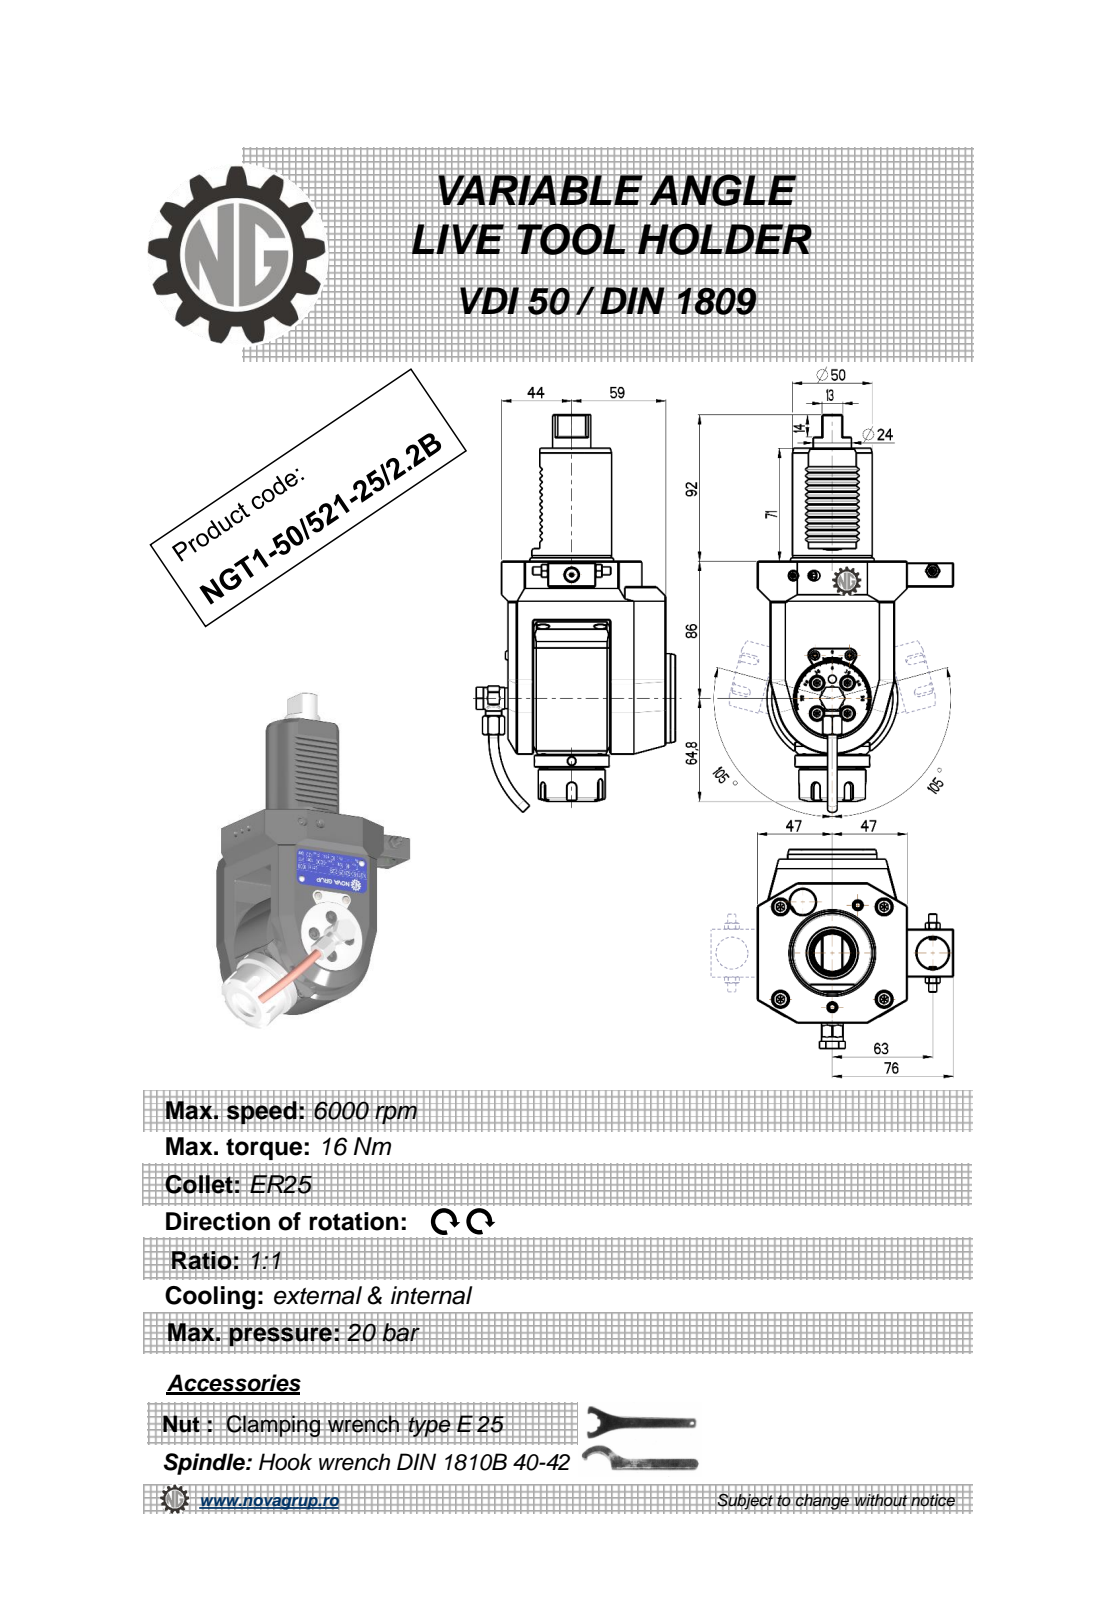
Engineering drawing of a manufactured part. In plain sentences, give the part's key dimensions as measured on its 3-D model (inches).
The part is named "NGT1_50_521_25_2_2B". Its 3-D file was written by "PRO/ENGINEER BY PARAMETRIC TECHNOLOGY CORPORATION, 2010280 (CONFIG_CONTROL_DESIGN)". It is 1 solid with 624 faces: 275 planar, 148 cylindrical and 201 other. Overall it measures 9.83 by 4.917 by 4.843 inches. Its volume is 62.79 cubic inches and its surface area 140.8 square inches. Round holes: 5 of diameter 0.157, 2 of diameter 0.15, 2 of diameter 0.197, 1 of diameter 0.118, 1 of diameter 0.244, 1 of diameter 0.354, 1 of diameter 0.374, 1 of diameter 0.394, 1 of diameter 0.433, 1 of diameter 0.787, 1 of diameter 0.799. Round bosses or shafts: 2 of diameter 0.236, 2 of diameter 0.224, 1 of diameter 2.205, 1 of diameter 1.969, 1 of diameter 1.85, 1 of diameter 1.654, 1 of diameter 1.378, 1 of diameter 0.945. Partial cylindrical surfaces (rounded edges, fillets, slot ends): 12 of radius 0.01, 12 of radius 0.012, 6 of radius 0.006, 5 of radius 0.118, 4 of radius 0.02, 2 of radius 0.031, 2 of radius 0.039, 2 of radius 0.394. The main face-to-face distances are 1.457, 3.898, 0.63, 0.315, 0.827, 0.236, 2.52, 4.134, 0.787, 3.071. The hole center spacings are 0.354, 4.618, 0.016, 0.709, 1.553, 1.929, 1.945, 2.48.
